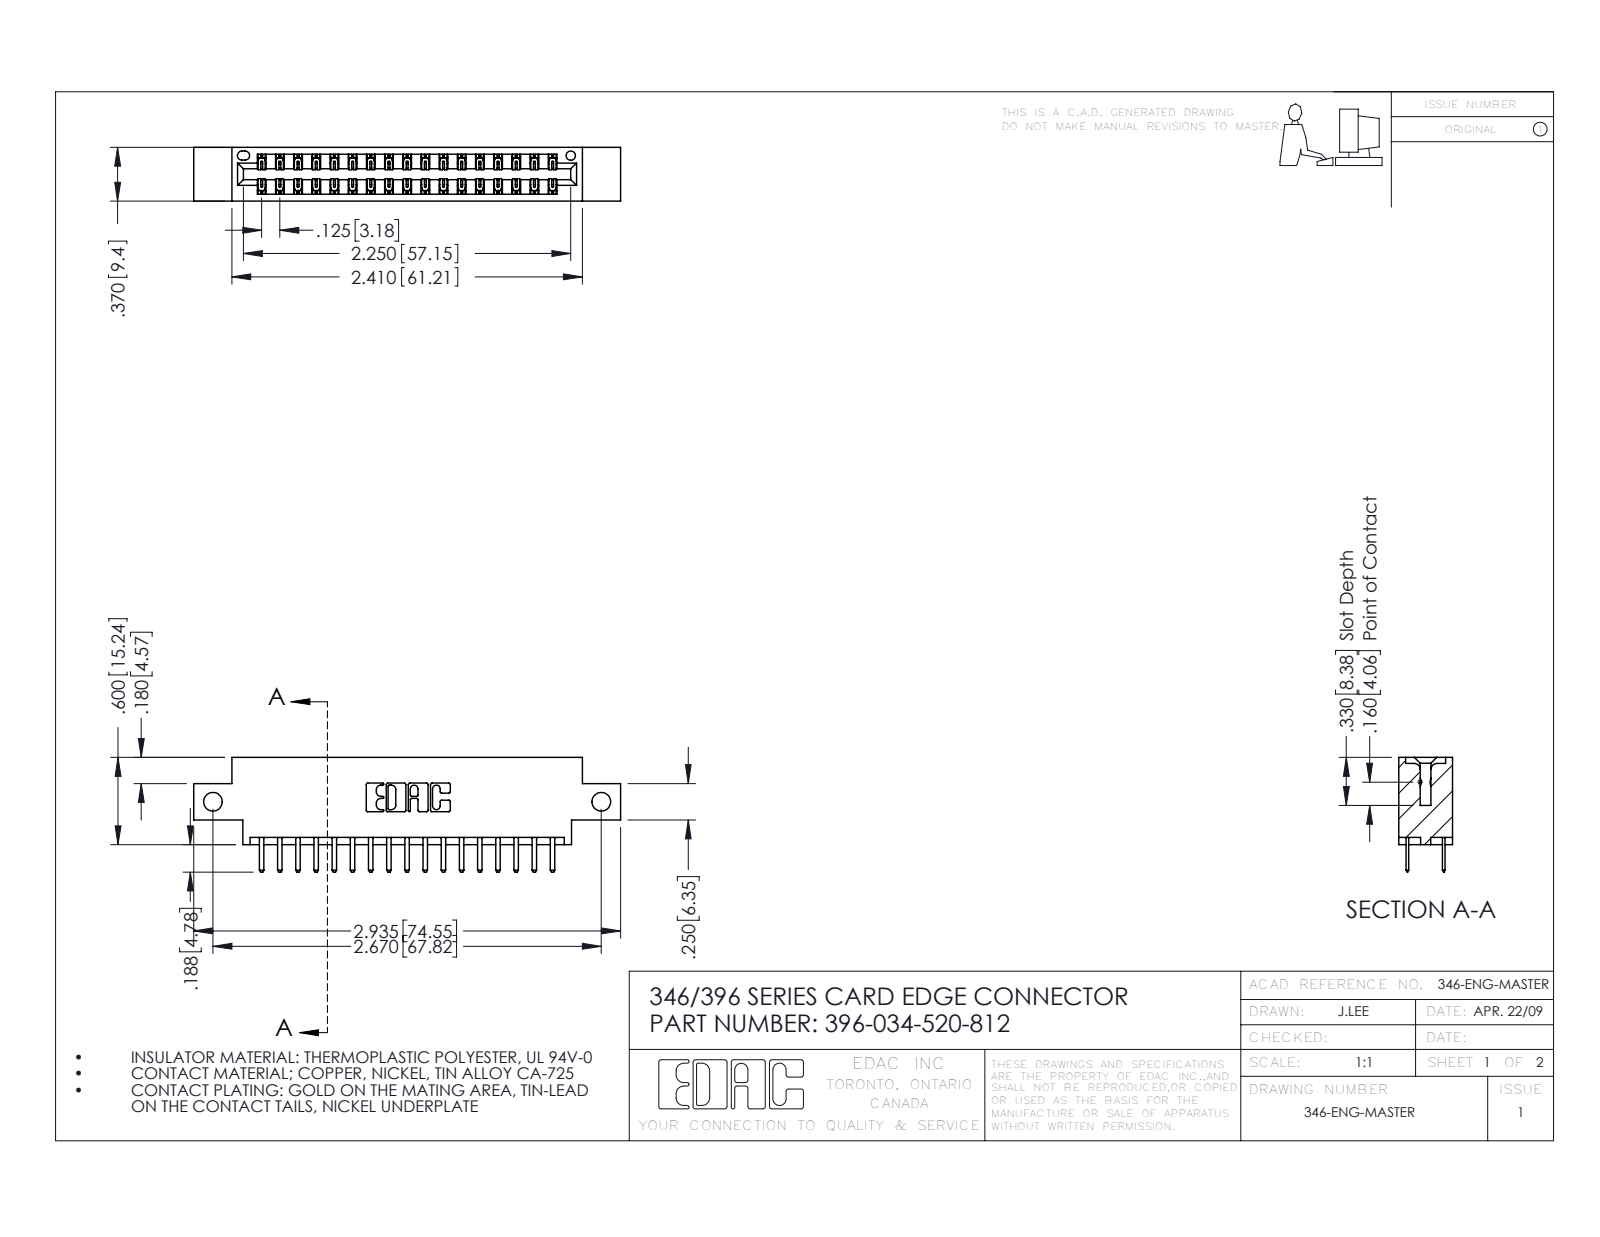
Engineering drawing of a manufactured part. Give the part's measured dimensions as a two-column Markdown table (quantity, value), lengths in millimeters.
| quantity | value |
| --- | --- |
| part name | 346 Part_0.170 Offset - Side Mount; 345-292-001_345-293-120; 396-034-520-812 |
| STEP written by | SolidWorks 2016 (CONFIG_CONTROL_DESIGN) |
| units | millimeters |
| bodies | 35 solids, 2030 faces (1338 planar, 692 cylindrical, 0 other) |
| overall size | 74.5 × 20 × 9.4 |
| volume | 6 820 mm³ |
| surface area | 8 987 mm² |
| round holes (diameter × count) | 3.3 × 2, 1.6 × 1 |
| partial cylindrical surfaces (radius × count) | 0.2 × 51, 0.3 × 38, 0.3 × 22, 0.2 × 6, 0.8 × 6, 0.7 × 3, 0.4 × 2, 0.6 × 2 |
| main face-to-face distances | 6.4, 1.2, 8.2, 9.4, 7, 1.8, 7.6, 0.6, 3.8, 5.6 |
| hole center spacings | 67.8 |
